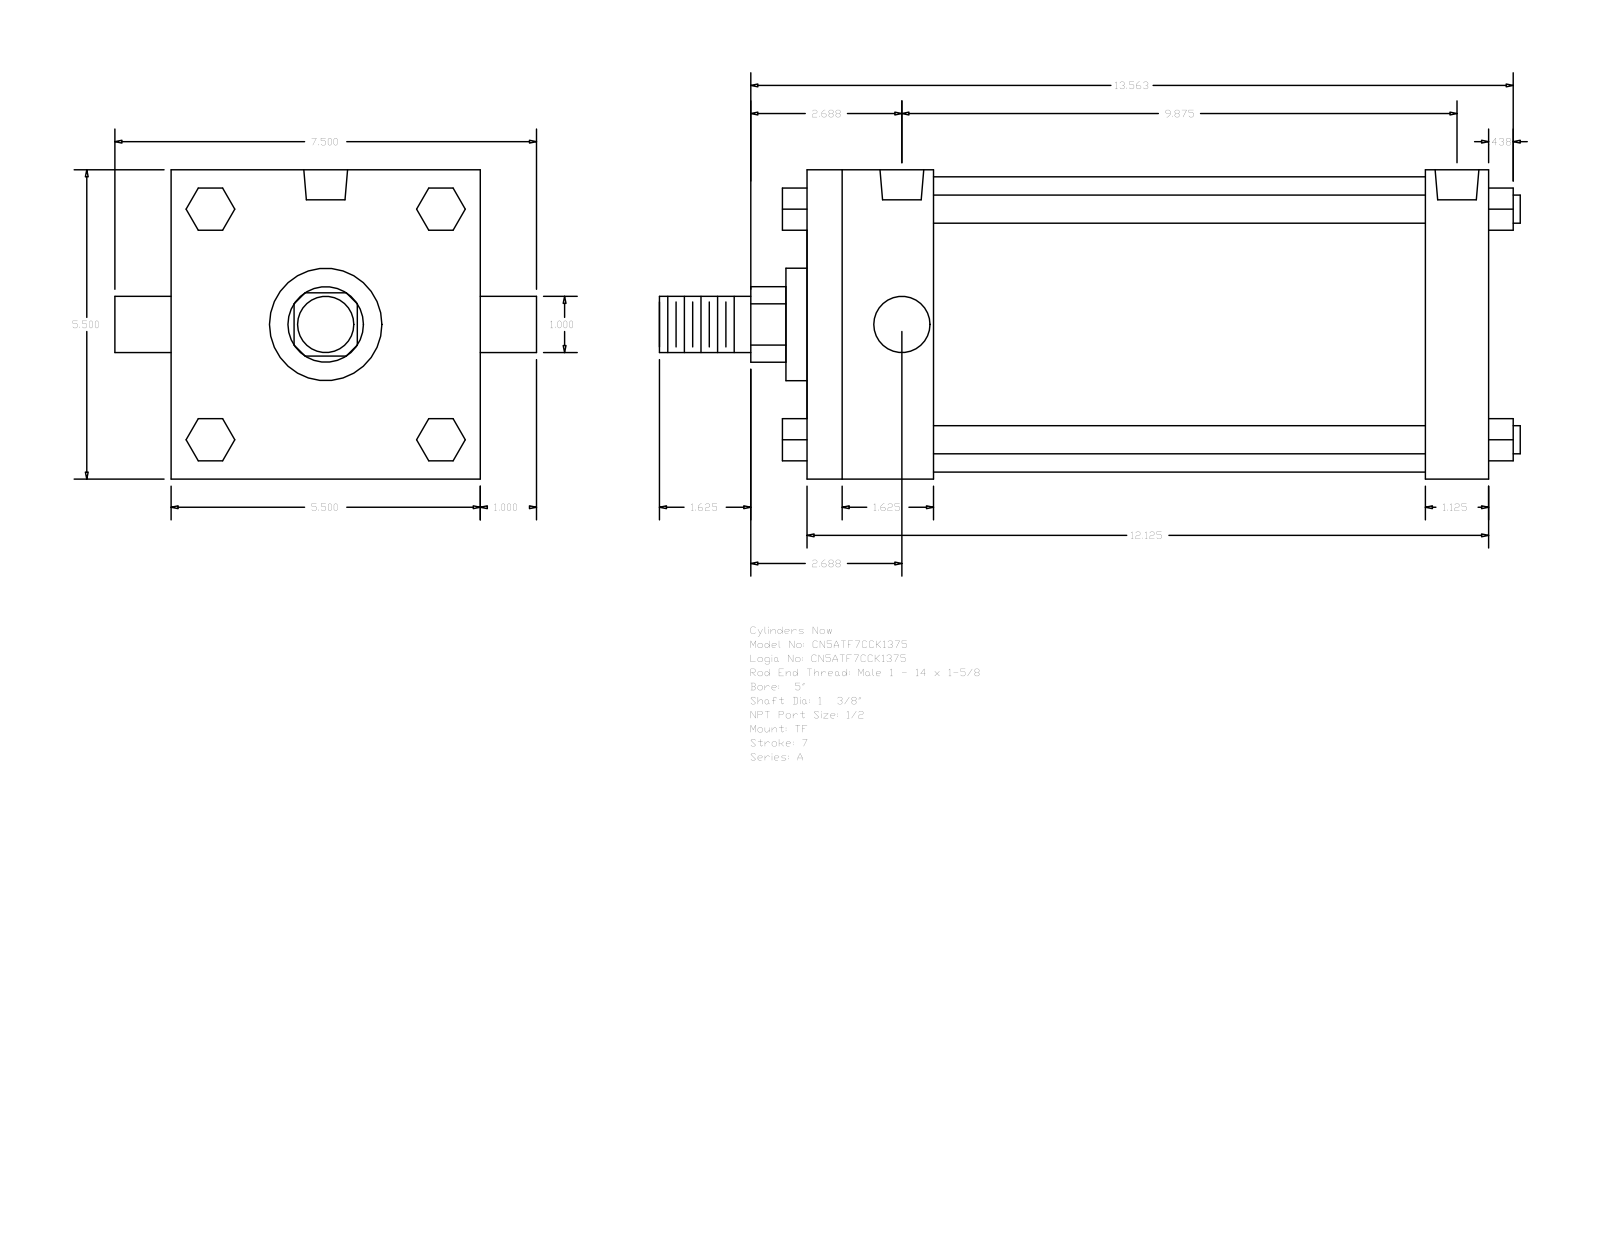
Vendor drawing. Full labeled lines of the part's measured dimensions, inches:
Part name (STEP PRODUCT): A_TF__0500_1.375
STEP written by: GSSL Pune (CONFIG_CONTROL_DESIGN)
Units: inches
Bodies: 0 solids, 120 faces (92 planar, 28 cylindrical, 0 other)
Overall size (bounding box): 15.313 × 7.5 × 5.5
Round holes (diameter × count): ⌀0.344 ×3, ⌀0.778 ×2
Round bosses / shafts (diameter × count): ⌀0.5 ×4, ⌀1 ×2, ⌀5.25 ×1, ⌀2 ×1, ⌀1.375 ×1
Partial cylindrical surfaces — rounded edges, fillets, slot ends (radius × count): R0.672 ×1
Main face-to-face distances: 5.5, 12.125, 2.25, 1.125, 11, 8.75, 9.875, 0.75, 2.05, 3.55
Hole centre spacings: 0.094, 9.781, 9.687, 9.875
